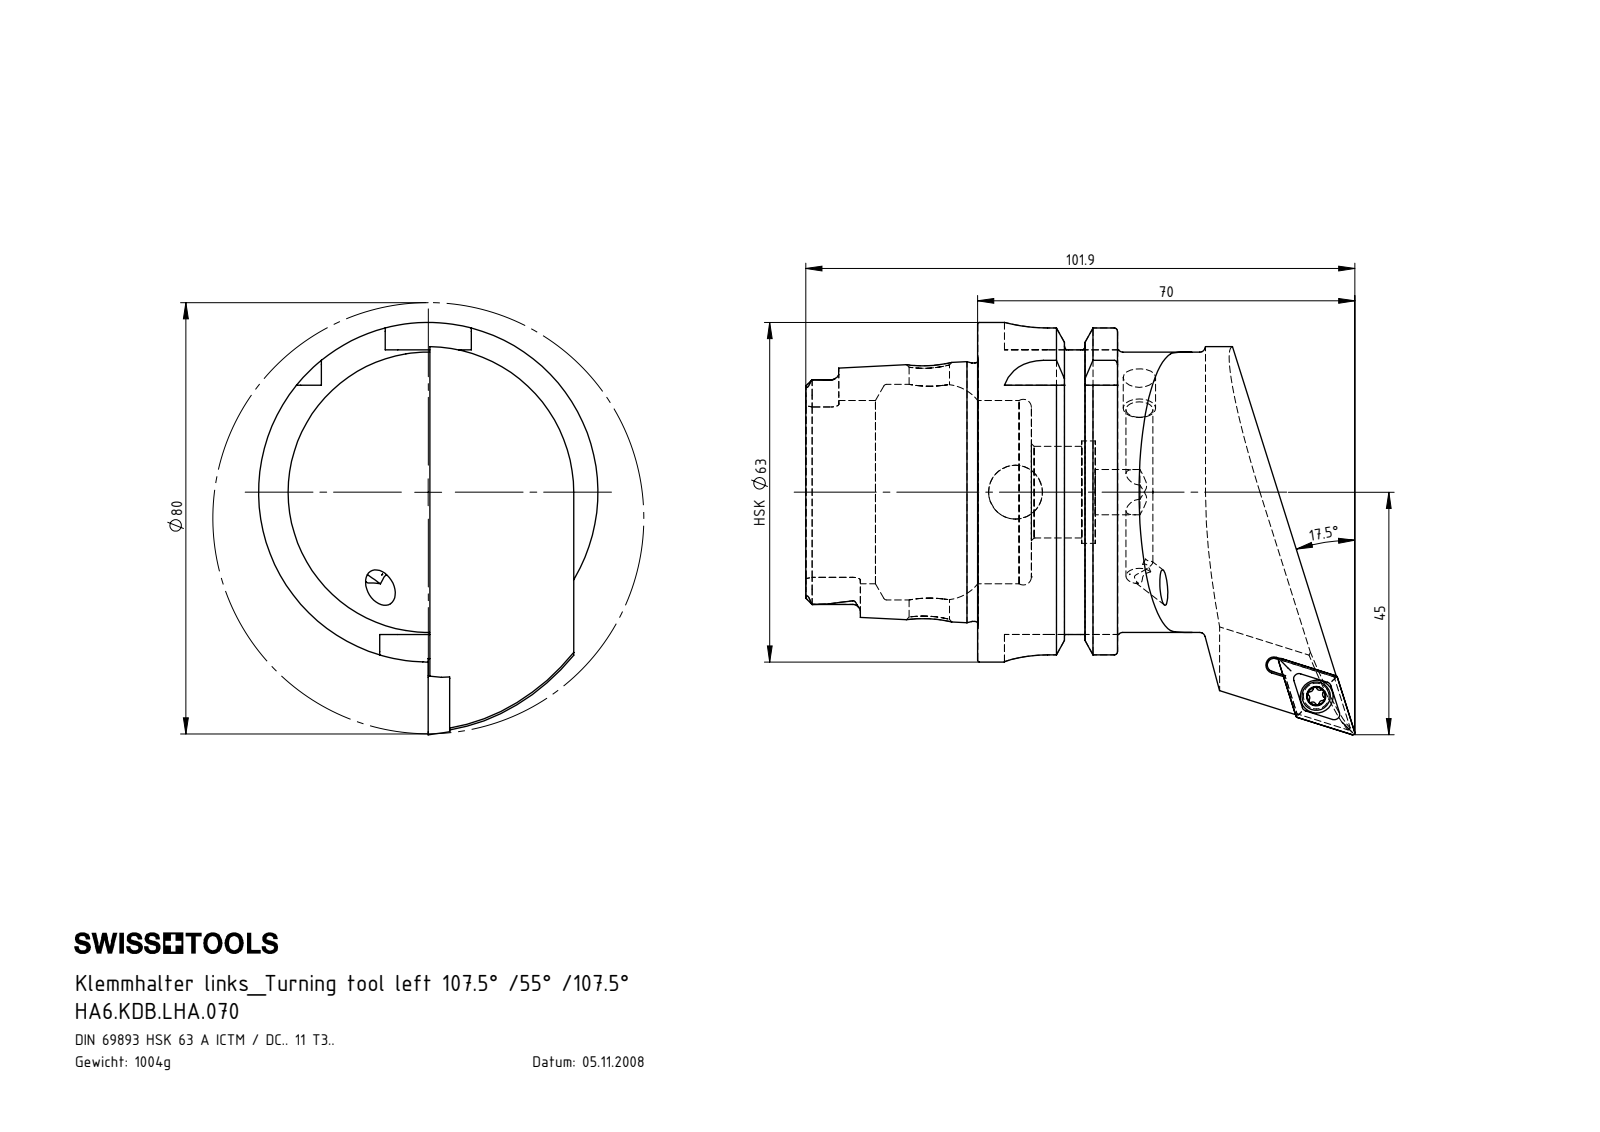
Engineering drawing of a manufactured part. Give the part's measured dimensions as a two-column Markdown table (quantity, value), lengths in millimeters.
| quantity | value |
| --- | --- |
| part name | HA6-KDB.LHA.070; KVT_MB_600_050; WCB-ER2.001.009_A; DCMT11T304 (+1 more) |
| STEP written by | SolidWorks 2012 (CONFIG_CONTROL_DESIGN) |
| units | millimeters |
| bodies | 5 solids, 313 faces (77 planar, 93 cylindrical, 143 other) |
| overall size | 101.91 × 76.5 × 63 |
| volume | 129 449 mm³ |
| surface area | 29 601 mm² |
| round holes (diameter × count) | 4.2 × 2, 3.3 × 1, 4 × 1, 4.4 × 1, 5 × 1, 6.1 × 1, 7.5 × 1, 8.4 × 1, 10 × 1, 17 × 1, 19 × 1, 34 × 1 |
| round bosses / shafts (diameter × count) | 63 × 1, 54.95 × 1, 52 × 1, 47.94 × 1, 5.25 × 1, 5 × 1, 4 × 1 |
| partial cylindrical surfaces (radius × count) | 0.34 × 6, 0.59 × 6, 1.4 × 6, 8 × 4, 2.82 × 2, 2.88 × 2, 1.25 × 1, 6 × 1 |
| main face-to-face distances | 25.95, 16, 9.95, 26.7, 31.9, 41.85, 57.85, 52.8, 21.8, 11.85 |
| hole center spacings | 67.44, 67.56 |
